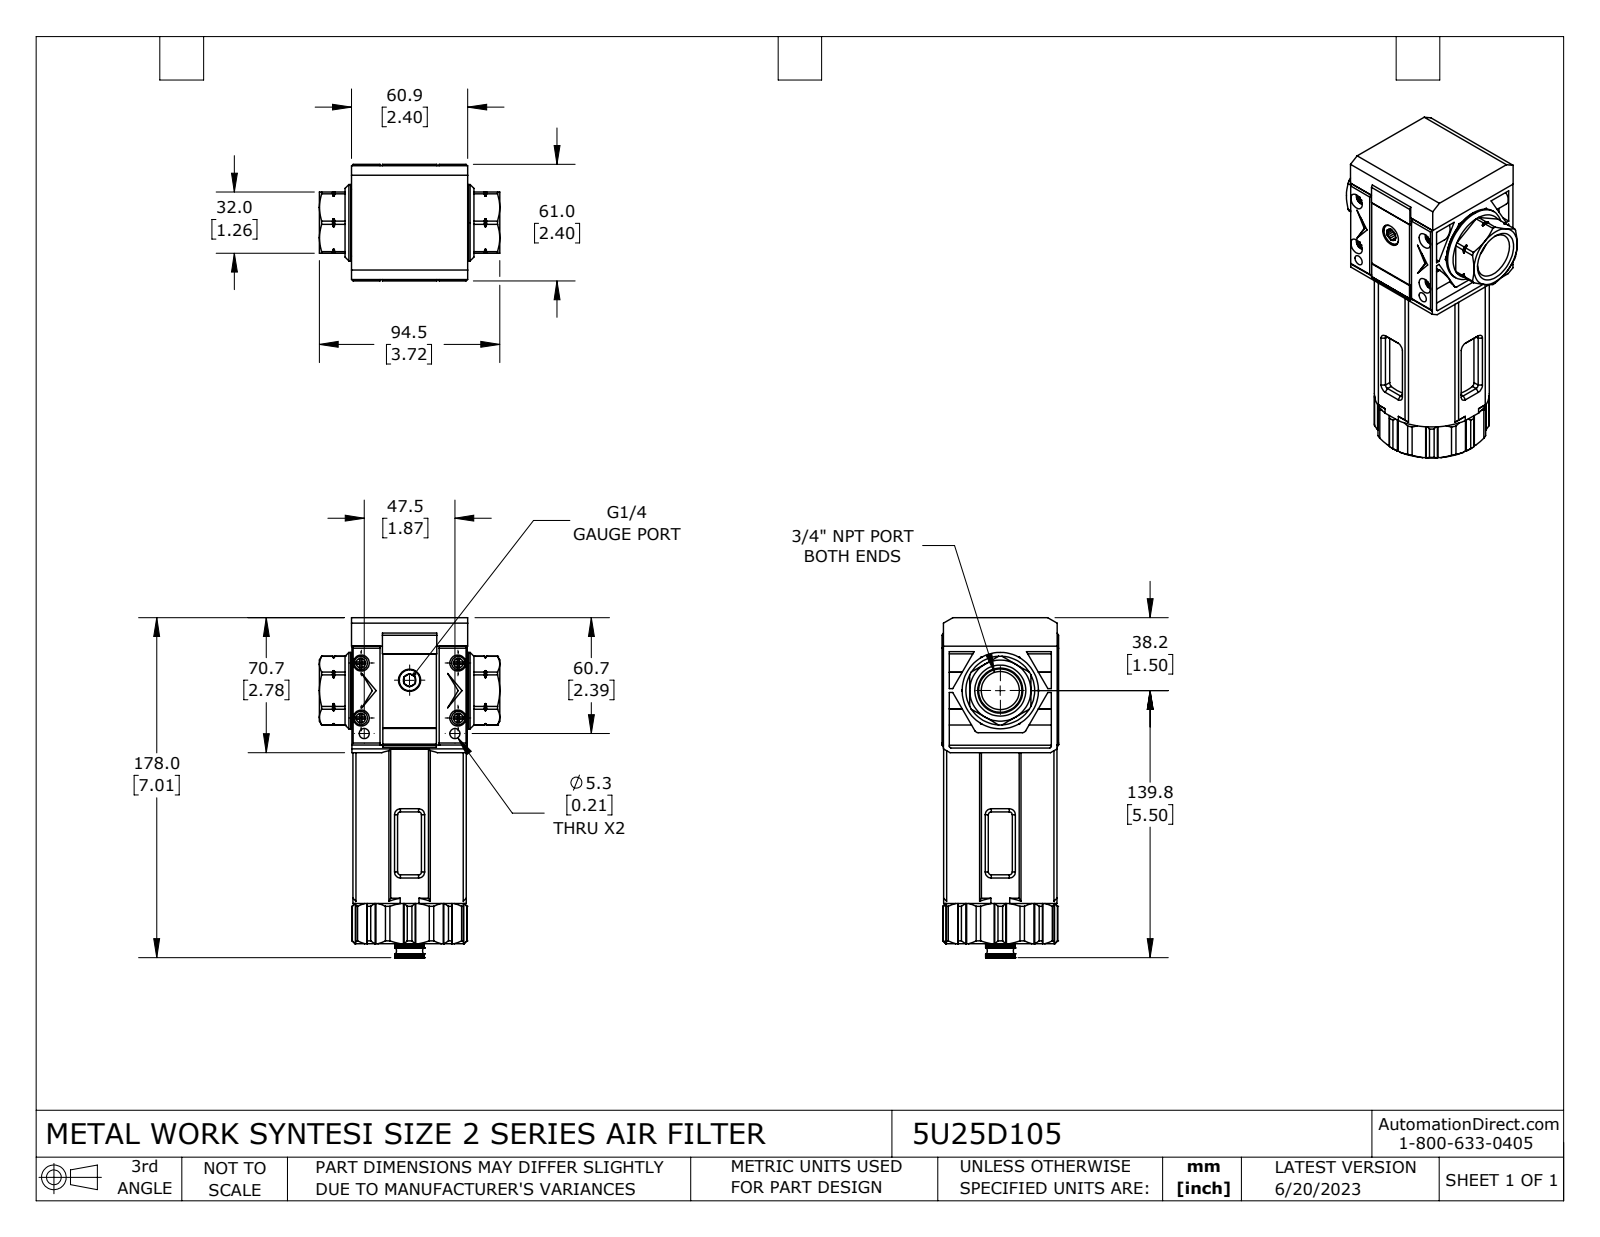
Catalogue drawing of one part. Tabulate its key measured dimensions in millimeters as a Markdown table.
| quantity | value |
| --- | --- |
| part name | 5U25D105 |
| STEP written by | SolidWorks 2021 (CONFIG_CONTROL_DESIGN) |
| units | millimeters |
| bodies | 14 solids, 1548 faces (975 planar, 303 cylindrical, 270 other) |
| overall size | 178 × 94.5 × 61 |
| volume | 406 200 mm³ |
| surface area | 127 500 mm² |
| round holes (diameter × count) | 3.3 × 4, 4.2 × 4, 8.4 × 4, 5.3 × 2, 3.2 × 1, 7 × 1, 8.7 × 1, 11.6 × 1, 20 × 1, 32 × 1, 49 × 1, 50 × 1 |
| round bosses / shafts (diameter × count) | 7 × 4, 4.8 × 4, 3.8 × 4, 40 × 1, 35 × 1, 31.7 × 1, 26.3 × 1, 23.5 × 1 |
| partial cylindrical surfaces (radius × count) | 0.5 × 16, 1.5 × 8, 4.9 × 4, 0.2 × 2, 2 × 2, 6.1 × 2, 3 × 1, 7 × 1 |
| main face-to-face distances | 60.7, 15, 134.7, 81.4, 53.3, 68.3, 28.7, 149.7, 55.7, 45.7 |
| hole center spacings | 8.3, 26.8, 28.8, 32.1, 36.7, 36.9, 49.7, 50.6 |
